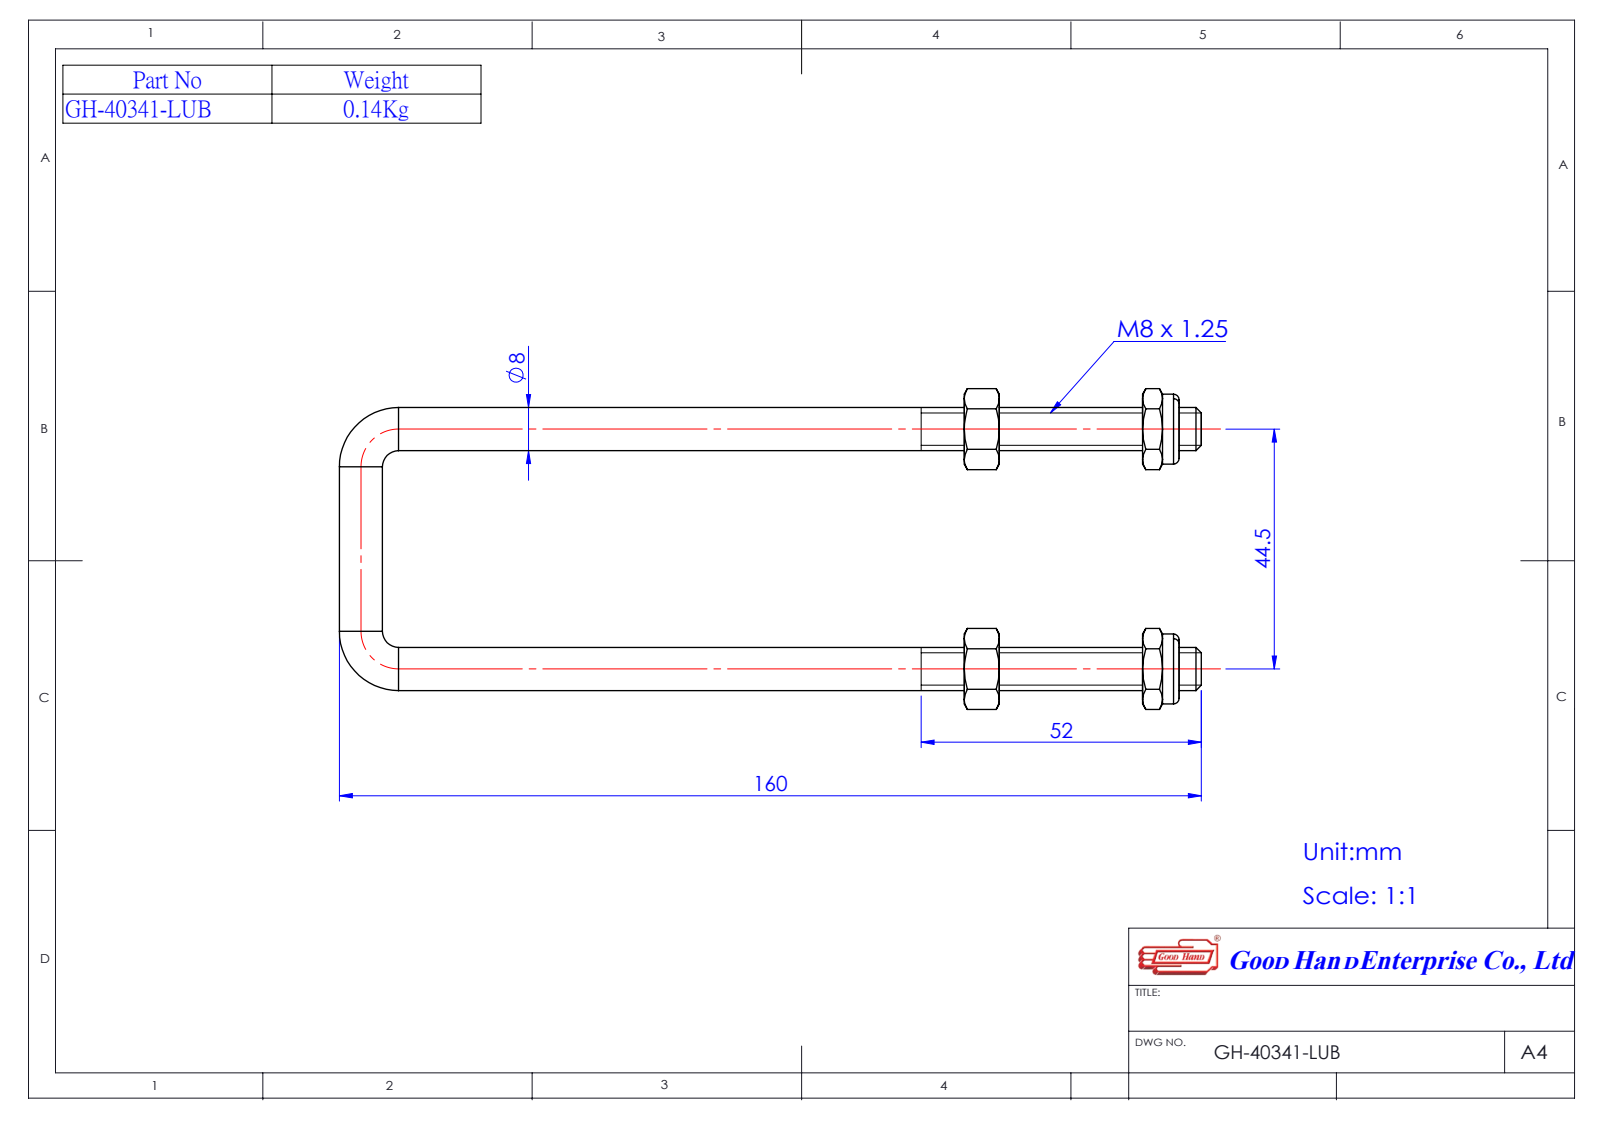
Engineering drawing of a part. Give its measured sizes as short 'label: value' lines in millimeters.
name: 14034144_160; Hexagon Nut_2_JIS_JIS B 1181 Hexagon nut - Class 2 Finished M8 --N; GH-40341-LUB
written by: SolidWorks 2016 (AUTOMOTIVE_DESIGN)
unit: mm
bodies: 5 solids, 132 faces (34 planar, 22 cylindrical, 76 other)
size: 160 × 59.51 × 13
volume: 20 412 mm³; area: 11 383 mm²
holes: 2× ⌀6.8, 2× ⌀8
bosses: 1× ⌀8
face distances: 13, 38.54, 32.98, 6.5, 51.54, 25.54, 39.48, 26.48, 44, 37.5
hole spacings: 44.5
